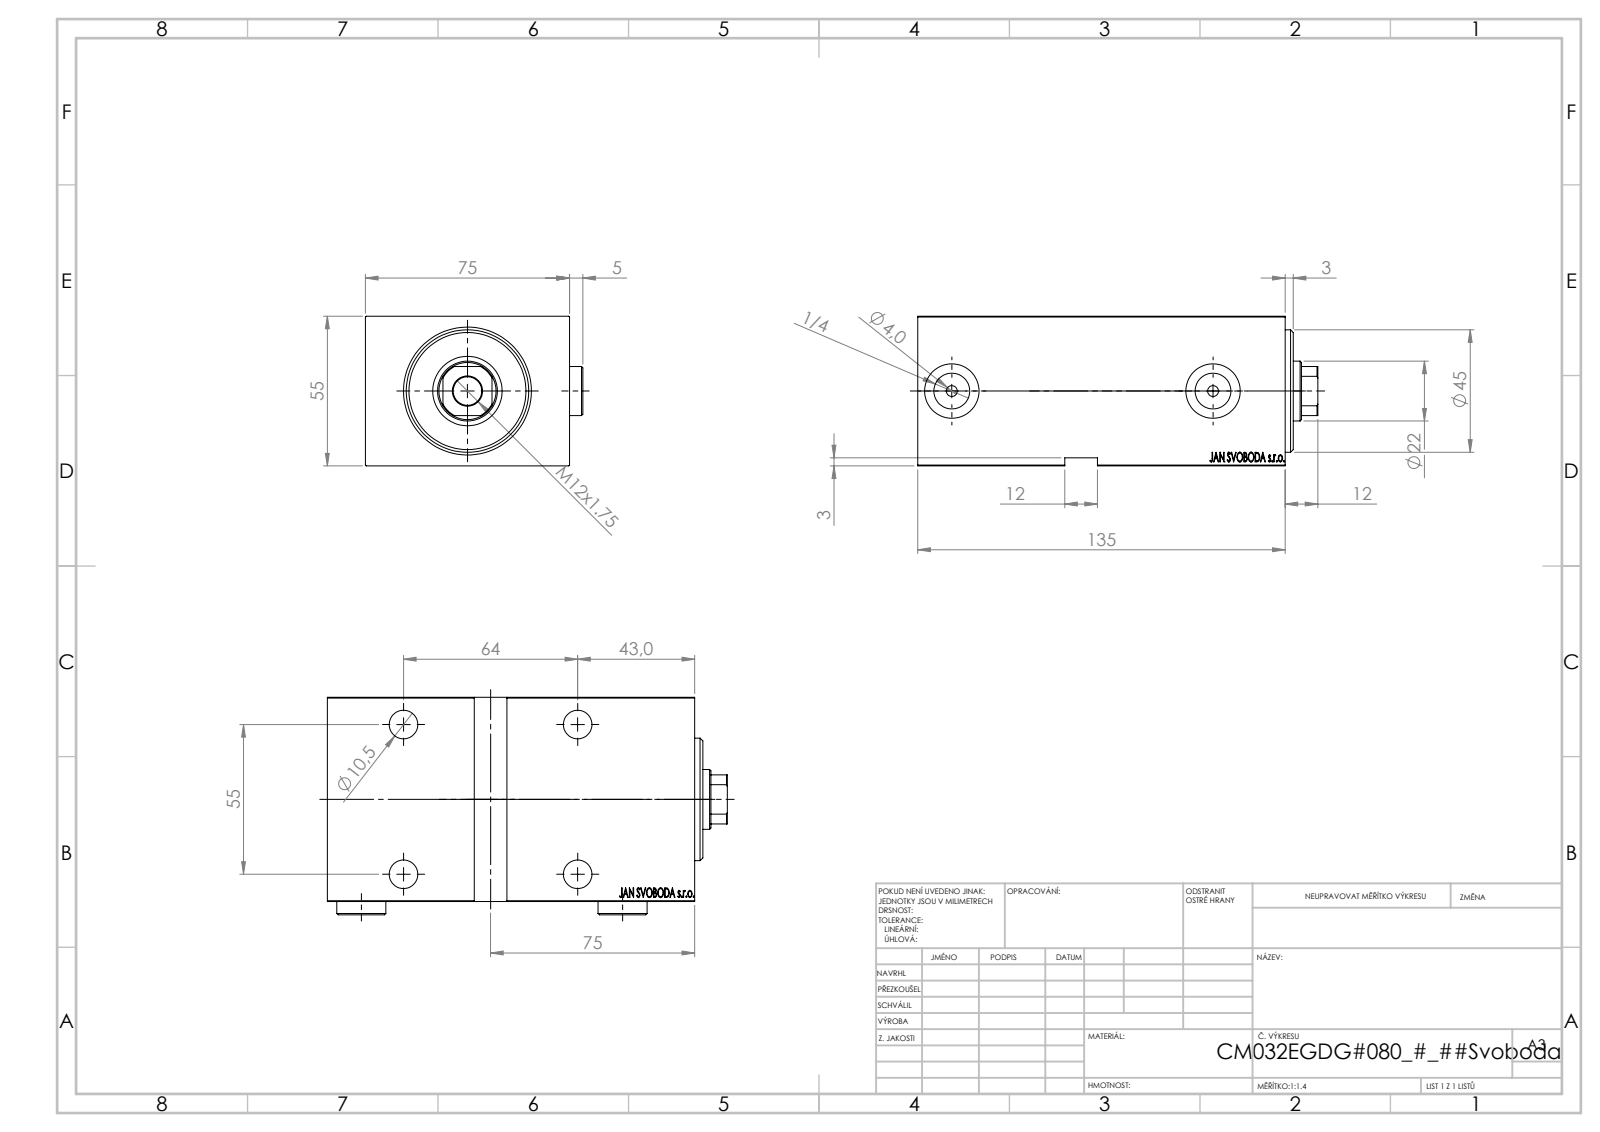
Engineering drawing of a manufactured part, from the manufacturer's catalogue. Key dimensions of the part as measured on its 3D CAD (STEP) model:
Part name (STEP PRODUCT): Zatka_OIL_PORT; V450CM_E_VCP; V450CM_E_Body; V450CM_VC_B
STEP written by: SolidWorks 2019 (CONFIG_CONTROL_DESIGN)
Units: millimetres
Bodies: 5 solids, 909 faces (445 planar, 66 cylindrical, 398 other)
Overall size (bounding box): 147 × 79.9 × 55
Volume: 496 699 mm³ · Surface area: 87 145 mm²
Round holes (diameter × count): ⌀10.5 ×5, ⌀16.5 ×4, ⌀4 ×2, ⌀13.16 ×2, ⌀20 ×2, ⌀22 ×1, ⌀25.5 ×1, ⌀32 ×1, ⌀45 ×1
Round bosses / shafts (diameter × count): ⌀18 ×2, ⌀34 ×1
Partial cylindrical surfaces — rounded edges, fillets, slot ends (radius × count): R10.5 ×1
Main face-to-face distances: 55, 75, 135, 3, 5, 10, 125, 130, 120, 74.9
Hole centre spacings: 55, 64, 84.39, 96
